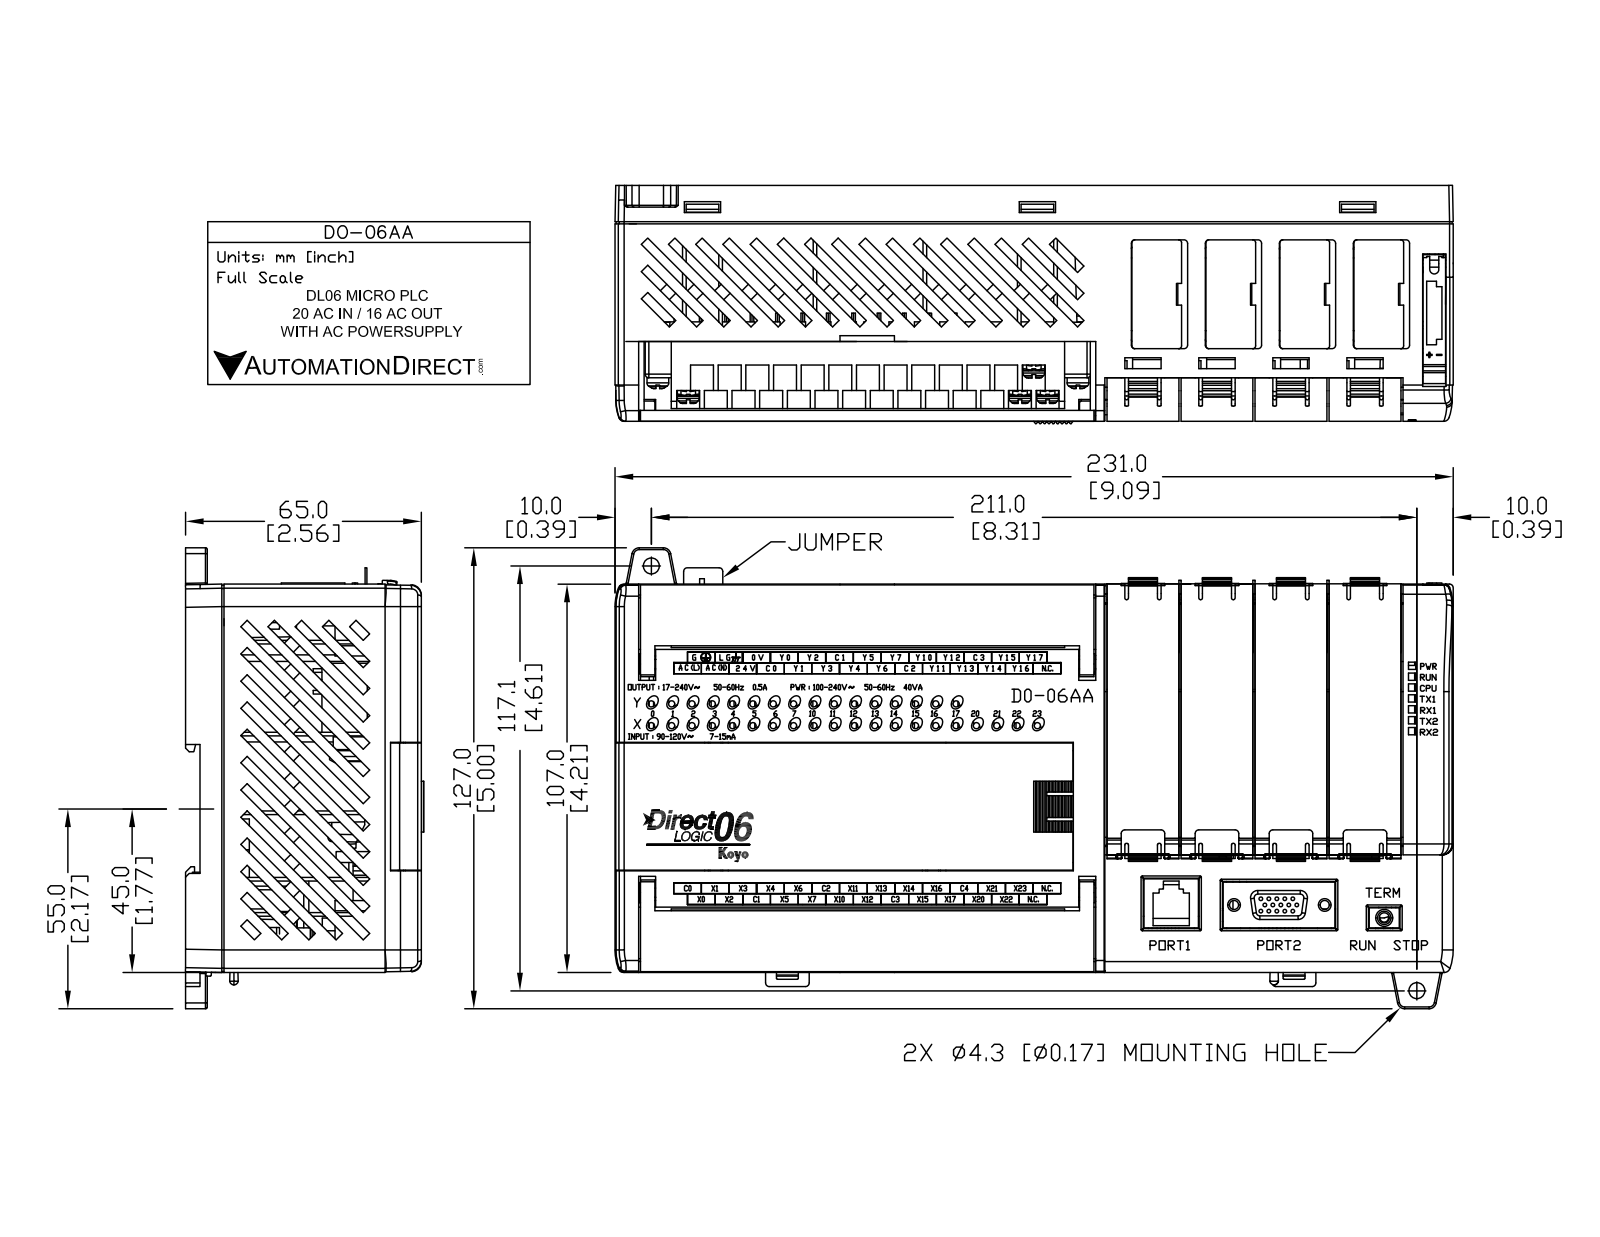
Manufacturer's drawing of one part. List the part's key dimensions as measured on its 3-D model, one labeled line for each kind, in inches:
Part name (STEP PRODUCT): D0-06AA
STEP written by: SolidWorks 2009 (AUTOMOTIVE_DESIGN)
Units: inches
Bodies: 1 solid, 1414 faces (930 planar, 189 cylindrical, 295 other)
Overall size (bounding box): 9.09 × 5.004 × 2.565
Volume: 16 in³ · Surface area: 309 in²
Round holes (diameter × count): ⌀0.118 ×4, ⌀0.079 ×2, ⌀0.17 ×2
Round bosses / shafts (diameter × count): ⌀0.185 ×54, ⌀0.25 ×4, ⌀0.175 ×1, ⌀0.14 ×1
Partial cylindrical surfaces — rounded edges, fillets, slot ends (radius × count): R0.05 ×8, R0.065 ×5, R0.062 ×4, R0.08 ×4, R0.038 ×2, R0.063 ×2, R0.076 ×1, R2.471 ×1
Main face-to-face distances: 0.088, 0.088, 2.472, 0.157, 2.315, 2.56, 9.002, 2.384, 0.245, 2.227
Hole centre spacings: 3.26, 4.612, 5.648, 0.676, 0.938, 1.399, 1.681, 2.203
